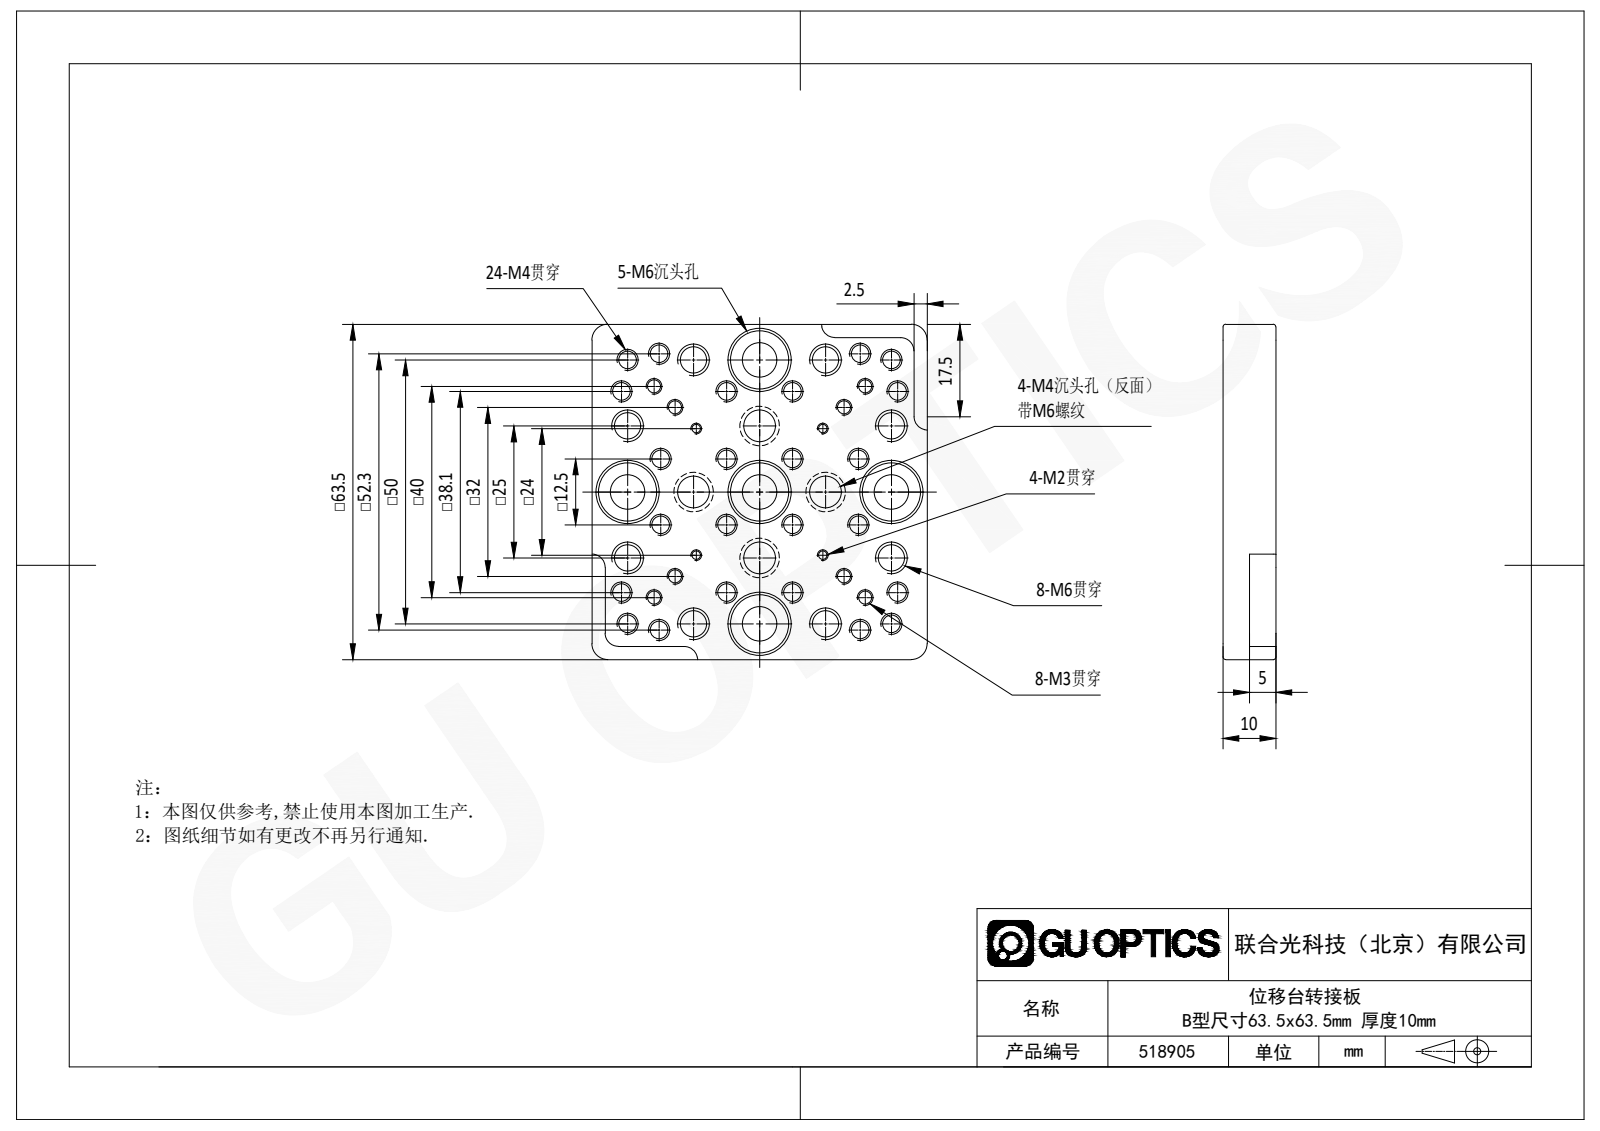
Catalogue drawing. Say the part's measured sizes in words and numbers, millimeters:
Its 3-D file was written by "SolidWorks 2020 (CONFIG_CONTROL_DESIGN)". It is 1 solid with 161 faces: 21 planar, 80 cylindrical and 60 other. Overall it measures 63.5 by 63.5 by 10 millimeters. Its volume is 29 898 cubic millimeters and its surface area 15 806 square millimeters. Round holes: 24 of diameter 3.3, 8 of diameter 2.5, 8 of diameter 5, 5 of diameter 6.5, 5 of diameter 11, 4 of diameter 1.6, 4 of diameter 6, 4 of diameter 7.5. Partial cylindrical surfaces (rounded edges, fillets, slot ends): 8 of radius 0.5, 6 of radius 2.5, 4 of radius 3. The main face-to-face distances are 10, 63.5, 5, 3, 7, 2.5, 61, 2, 58.5, 4.6. The hole center spacings are 12.5, 19.76, 27.95, 25, 8.84, 31.87, 19.75, 20.05.
